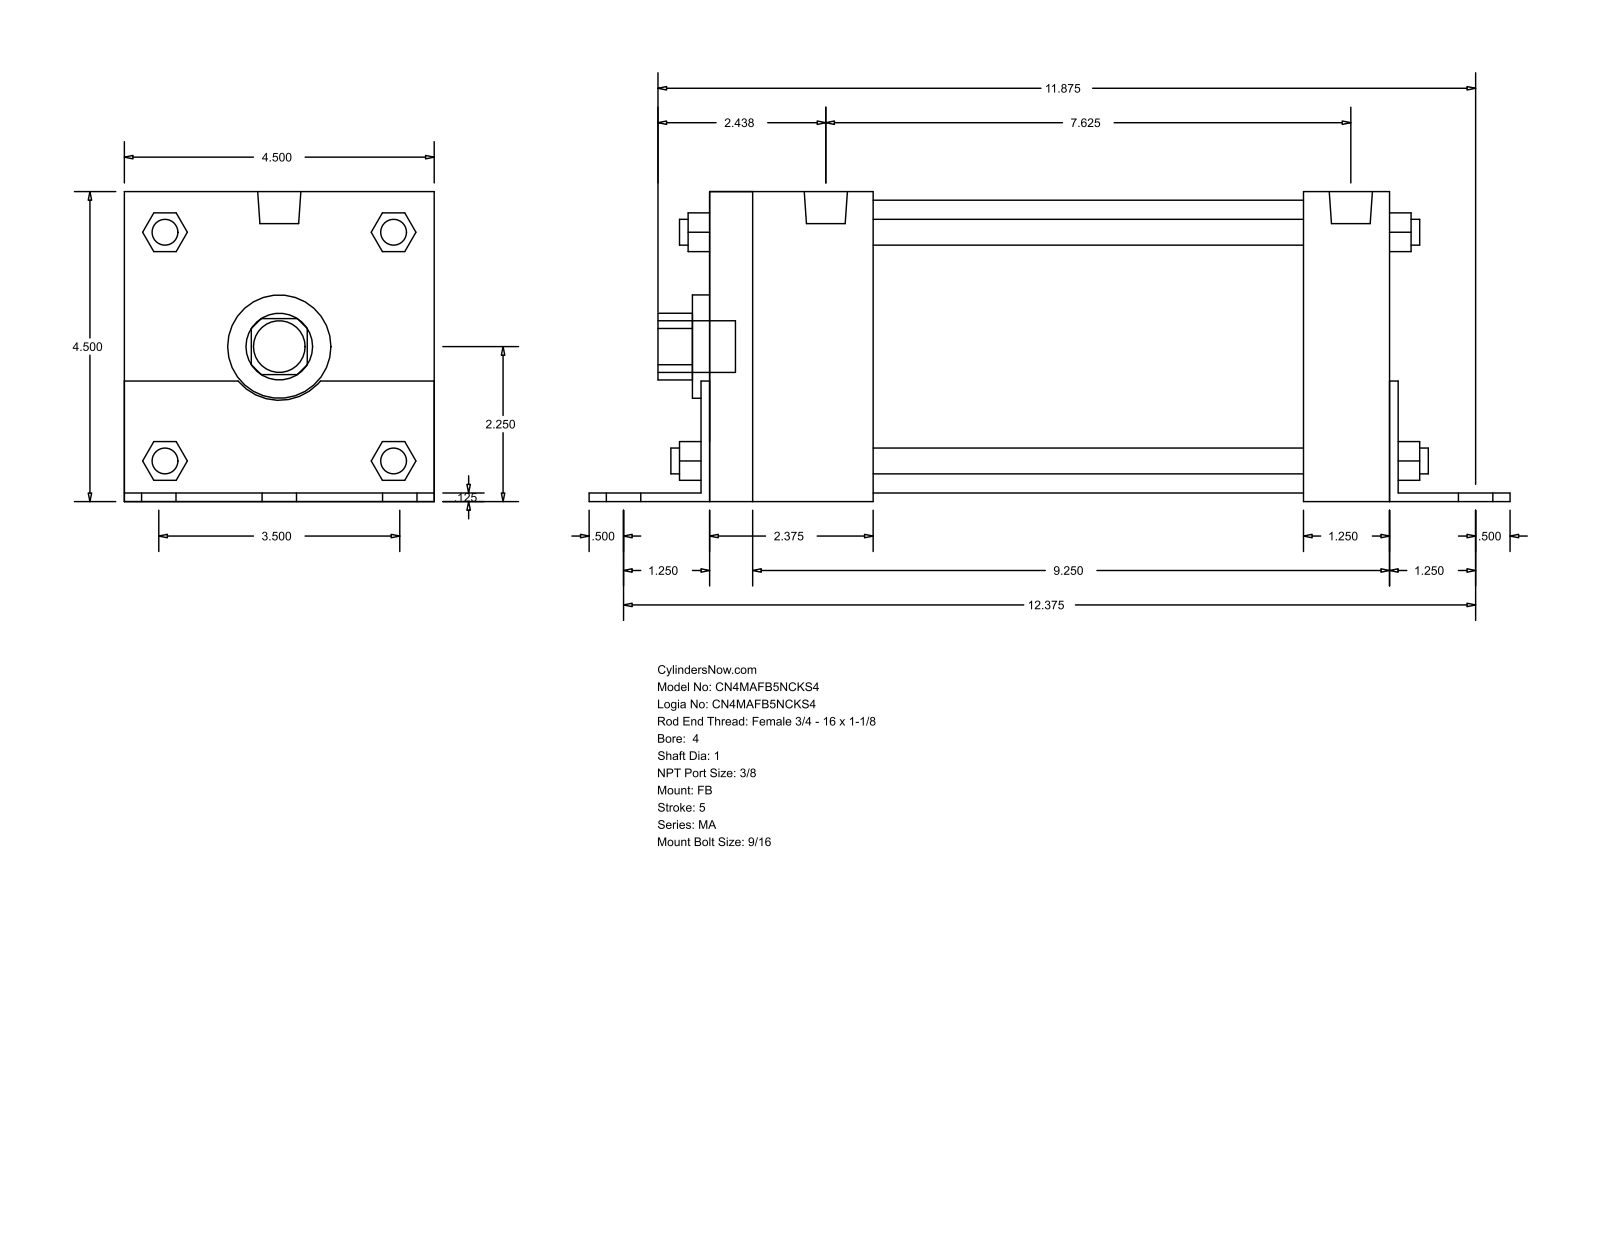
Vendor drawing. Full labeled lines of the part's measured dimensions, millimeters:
Part name (STEP PRODUCT): MA_FB__0400_1
STEP written by: GSSL Pune (CONFIG_CONTROL_DESIGN)
Units: millimetres
Bodies: 0 solids, 140 faces (105 planar, 35 cylindrical, 0 other)
Overall size (bounding box): 339.73 × 114.35 × 114.3
Round holes (diameter × count): ⌀25.4 ×1, ⌀38.1 ×1, ⌀107.95 ×1
Round bosses / shafts (diameter × count): ⌀14.29 ×6, ⌀11.11 ×4, ⌀9.53 ×4, ⌀15.93 ×2, ⌀19.05 ×1
Partial cylindrical surfaces — rounded edges, fillets, slot ends (radius × count): R12.29 ×1, R19.81 ×1
Main face-to-face distances: 114.3, 3.17, 114.35, 254, 3.12, 111.18, 250.83, 257.17, 34.93, 222.24
